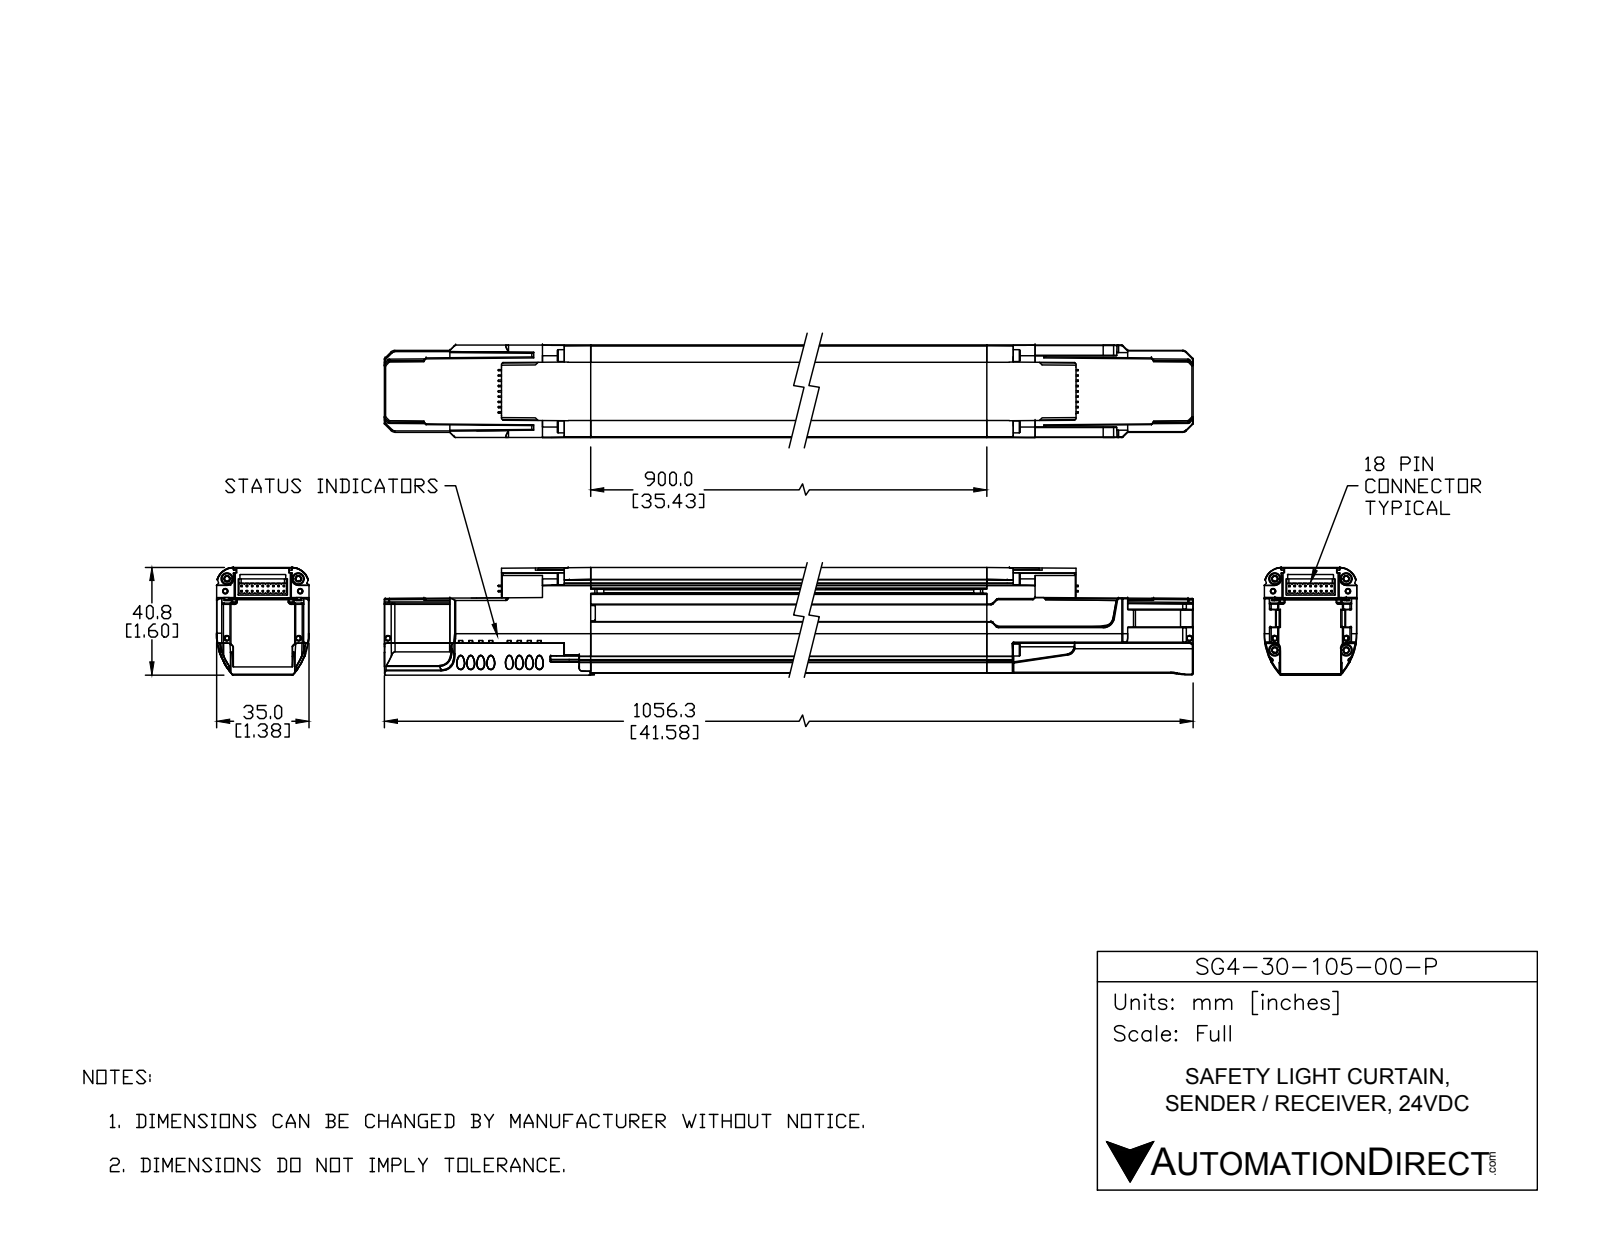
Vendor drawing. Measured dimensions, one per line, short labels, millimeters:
name: SG4-30-105-OO-P
written by: SolidWorks 2017 (AUTOMOTIVE_DESIGN)
unit: mm
bodies: 16 solids, 534 faces (362 planar, 110 cylindrical, 62 other)
size: 1056.2 × 65.5 × 51.4
volume: 1 292 000 mm³; area: 285 100 mm²
holes: 6× ⌀1.8, 4× ⌀2.5, 4× ⌀4.2, 4× ⌀5.3, 4× ⌀6.6, 1× ⌀1.7, 1× ⌀1.7
bosses: 4× ⌀10, 4× ⌀5
rounds: 16× R2.7, 8× R3, 4× R2.5, 4× R2.8, 2× R2, 2× R3, 2× R3.1, 2× R3.2
face distances: 1.5, 2.1, 0.6, 37.8, 37.2, 39.4, 26.8, 12.2, 25, 25.6
hole spacings: 14.5, 859.9, 0.5, 5.2, 5.3, 5.3, 5.8, 18
